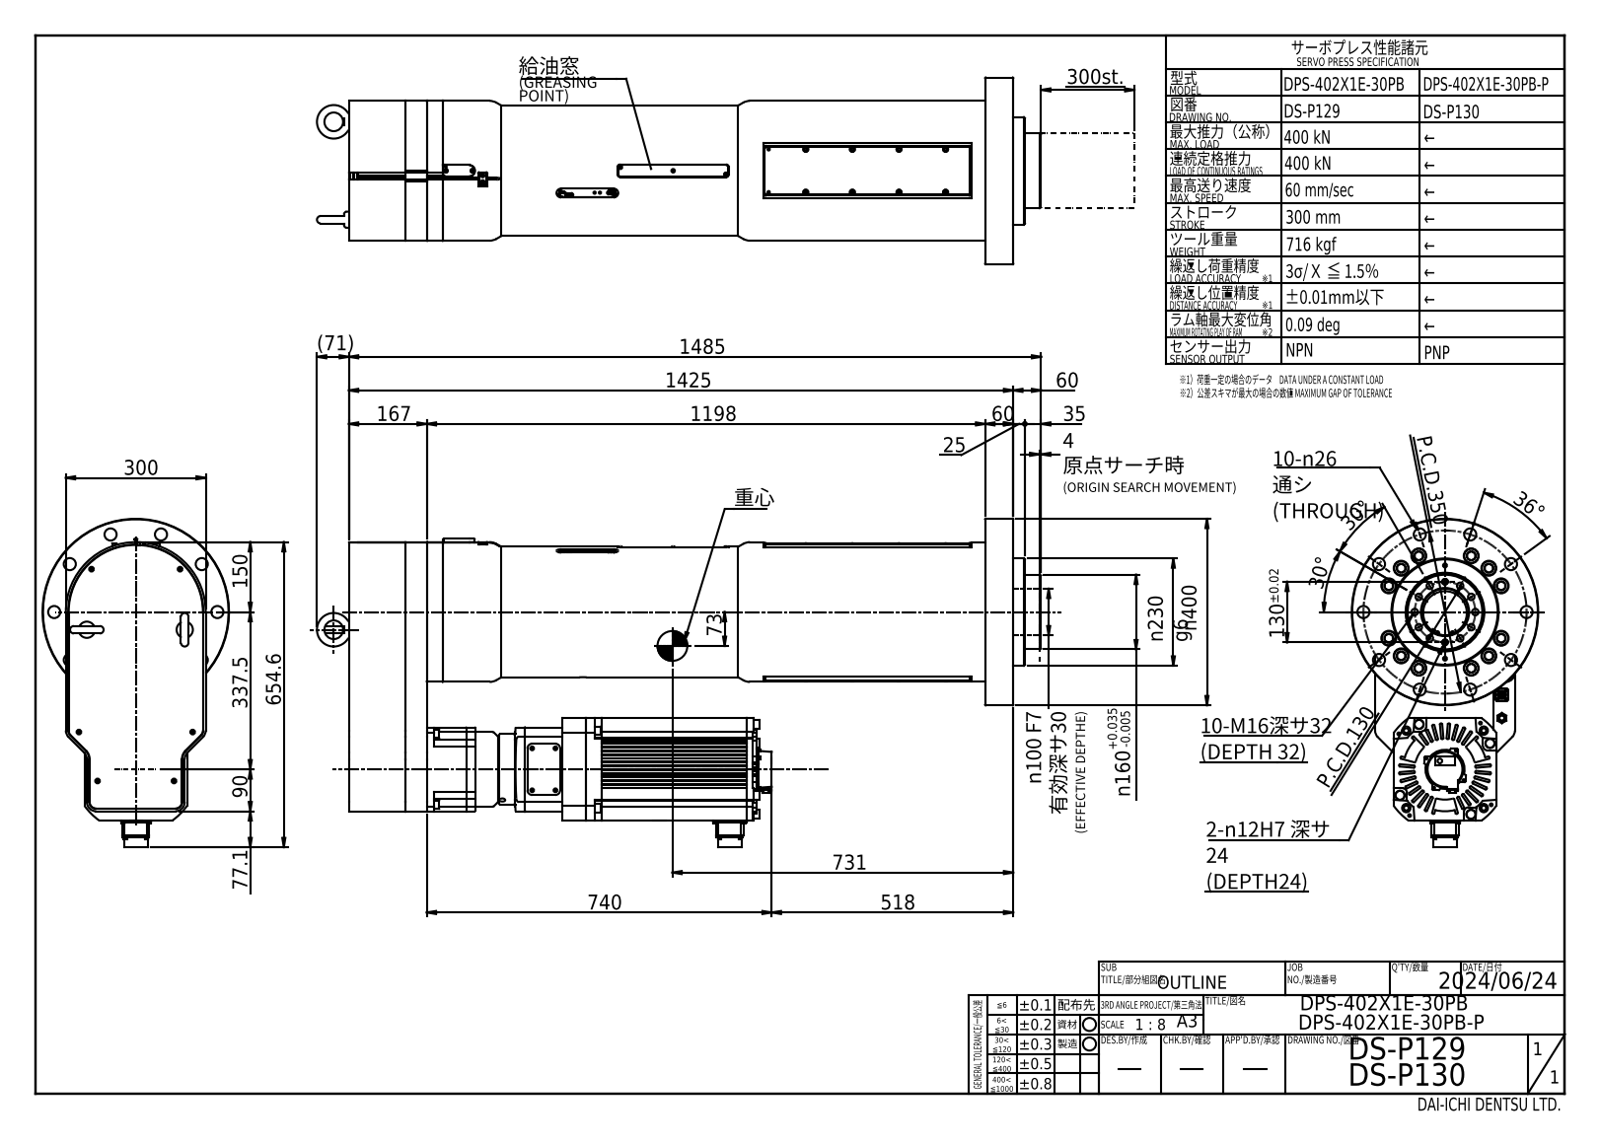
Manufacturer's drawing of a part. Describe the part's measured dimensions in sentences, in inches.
The part is named "DPS-402X1E-30FB(DS-P127)_OUTLINE_20240717". Its 3-D file was written by "Autodesk Inventor 2023 (CONFIG_CONTROL_DESIGN)". It is 1 solid with 2840 faces: 1723 planar, 594 cylindrical and 523 other. Overall it measures 61.165 by 27.739 by 15.748 inches. Its volume is 8 391 cubic inches and its surface area 4 639 square inches. Round holes: 14 of diameter 0.433, 12 of diameter 1.26, 10 of diameter 0.551, 10 of diameter 1.024, 6 of diameter 0.197, 4 of diameter 0.122, 4 of diameter 0.126, 4 of diameter 0.236, 4 of diameter 0.335, 4 of diameter 0.402, 3 of diameter 0.047, 3 of diameter 0.472. Round bosses or shafts: 15 of diameter 0.394, 12 of diameter 1.181, 9 of diameter 0.709, 8 of diameter 0.315, 8 of diameter 0.276, 7 of diameter 0.039, 4 of diameter 0.787, 4 of diameter 0.748. Partial cylindrical surfaces (rounded edges, fillets, slot ends): 64 of radius 0.098, 21 of radius 0.118, 20 of radius 0.02, 18 of radius 0.394, 8 of radius 0.197, 8 of radius 0.787, 6 of radius 0.079, 5 of radius 0.157. The main face-to-face distances are 0.787, 2.362, 7.874, 0.276, 8.386, 1.575, 7.598, 0.512, 56.047, 8.661. The hole center spacings are 6.89, 1.819, 3.937, 4.258, 5.236, 6.007, 7.405, 8.579.
